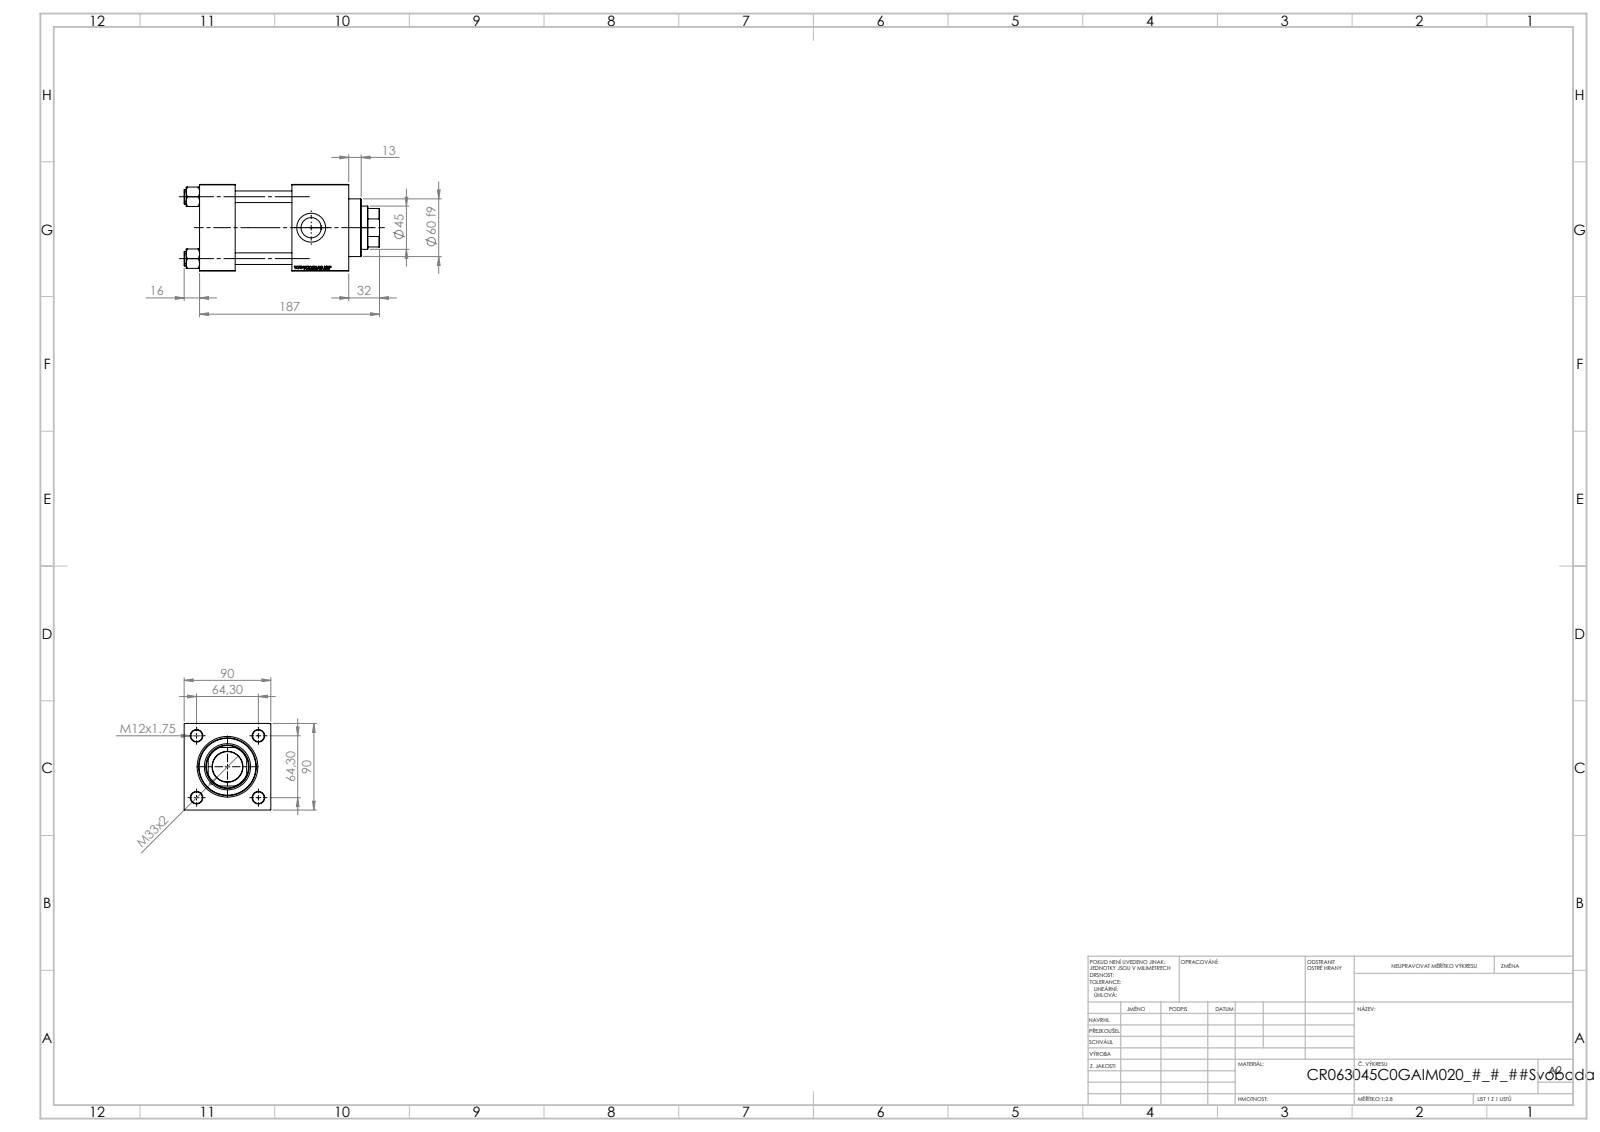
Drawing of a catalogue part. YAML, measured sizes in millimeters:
part_name: "V215_VC_A; V215CR_C_TYCINKA; NUT_M5_C; V215CR_VCP_C (+1 more)"
step_written_by: "SolidWorks 2019 (CONFIG_CONTROL_DESIGN)"
units: millimeters
bodies: {solids: 11, faces: 1146, planar: 525, cylindrical: 85, other: 536}
overall_size: [203, 90, 90]
volume: 997843
surface_area: 189935
round_holes:
  - {diameter: 12, count: 4}
  - {diameter: 7, count: 2}
  - {diameter: 20.96, count: 2}
  - {diameter: 30, count: 2}
  - {diameter: 31.5, count: 1}
  - {diameter: 45, count: 1}
  - {diameter: 48, count: 1}
  - {diameter: 50, count: 1}
  - {diameter: 60, count: 1}
  - {diameter: 63, count: 1}
round_bosses_or_shafts:
  - {diameter: 15, count: 4}
  - {diameter: 69, count: 1}
partial_cylinders:
  - {radius: 22, count: 1}
face_to_face_distances: [90, 59, 37, 96, 155, 118, 126.3, 89.3, 30.3, 28.7]
hole_center_spacings: [45.47, 64.3, 90.93]
